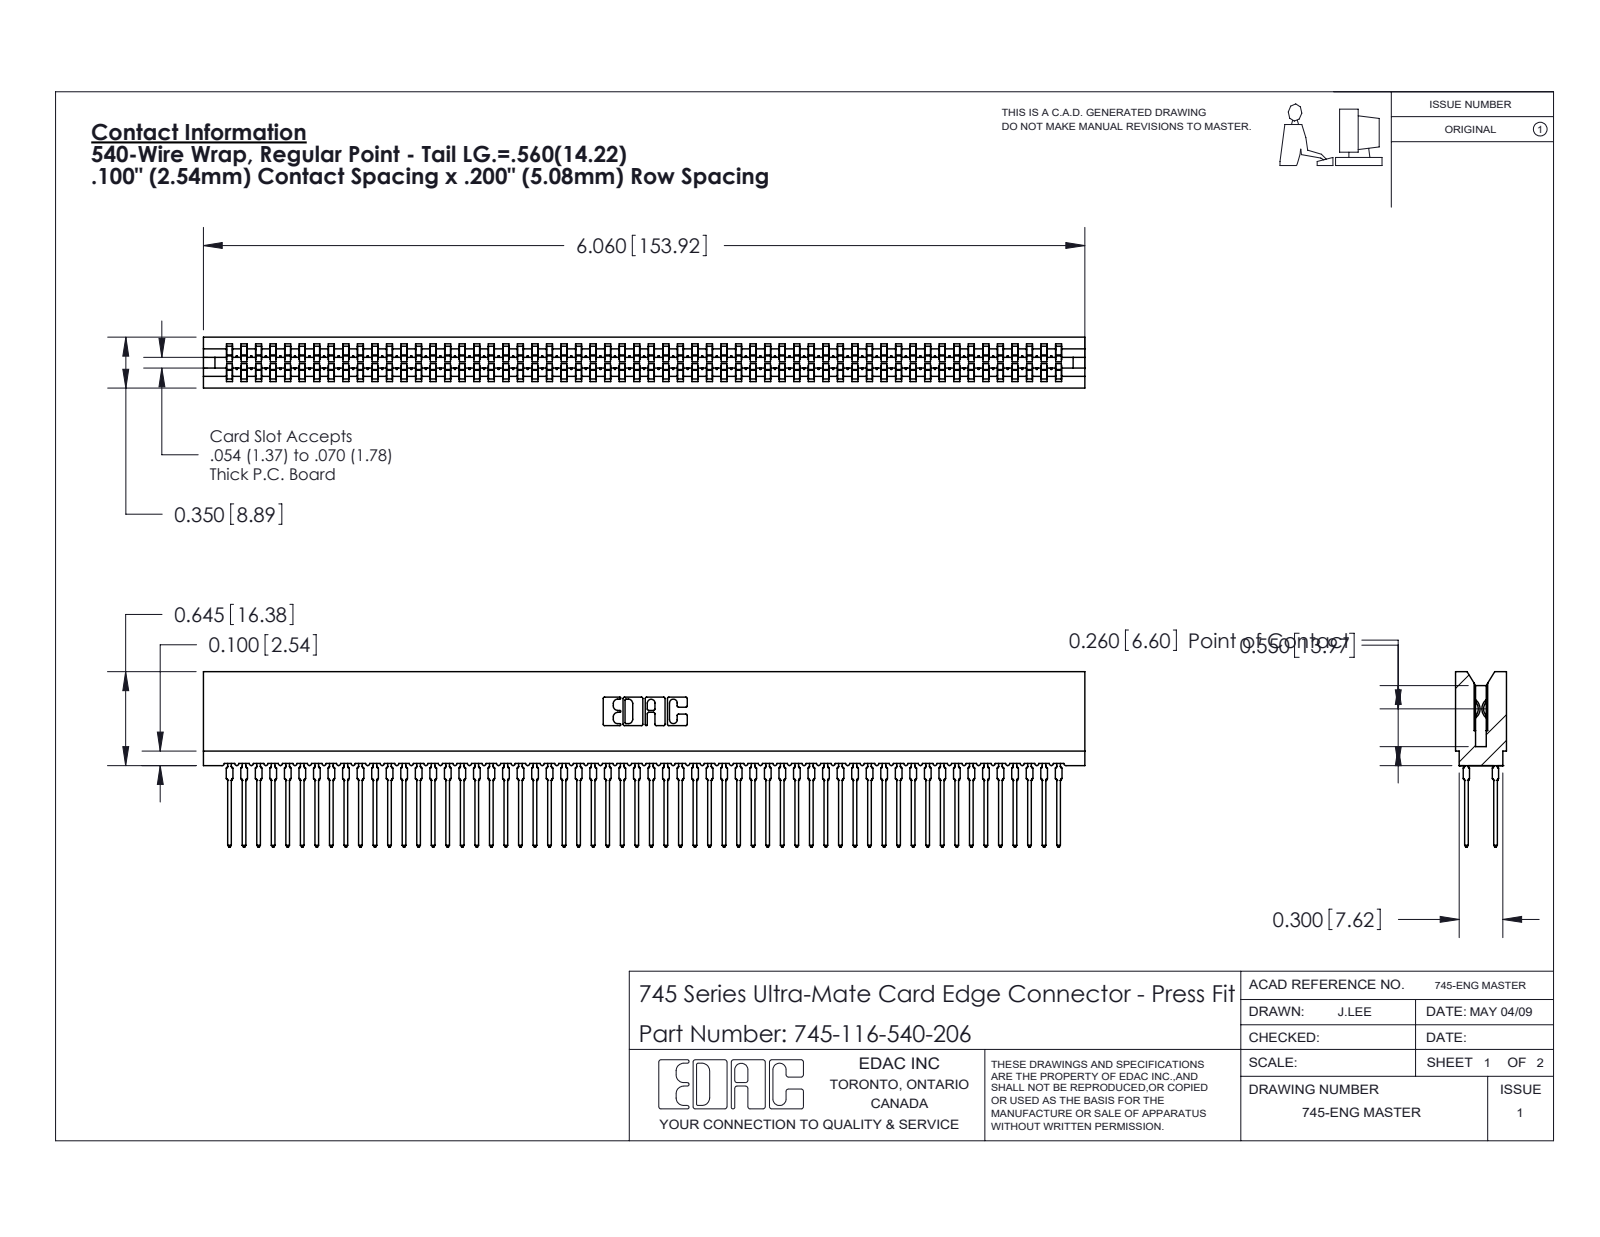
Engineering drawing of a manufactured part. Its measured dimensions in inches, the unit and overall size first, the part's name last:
Units: inches
Overall size (bounding box): 6.06 × 1.206 × 0.35
Partial cylindrical surfaces — rounded edges, fillets, slot ends (radius × count): R0.021 ×232, R0.015 ×116, R0.01 ×22, R0.005 ×8, R0.011 ×8, R0.007 ×6, R0.031 ×6, R0.026 ×3
Main face-to-face distances: 0.063, 0.287, 0.35, 0.045, 0.305, 0.018, 0.243, 0.2, 0.138, 0.212
Volume: 0.86 in³ · Surface area: 47.08 in²
Bodies: 117 solids, 10478 faces (5392 planar, 2070 cylindrical, 3016 other)
Part name (STEP PRODUCT): 745-292-001_540; 745 Part_Insulator Option - 06; 745-116-540-206
STEP written by: SolidWorks 2020 (CONFIG_CONTROL_DESIGN)
